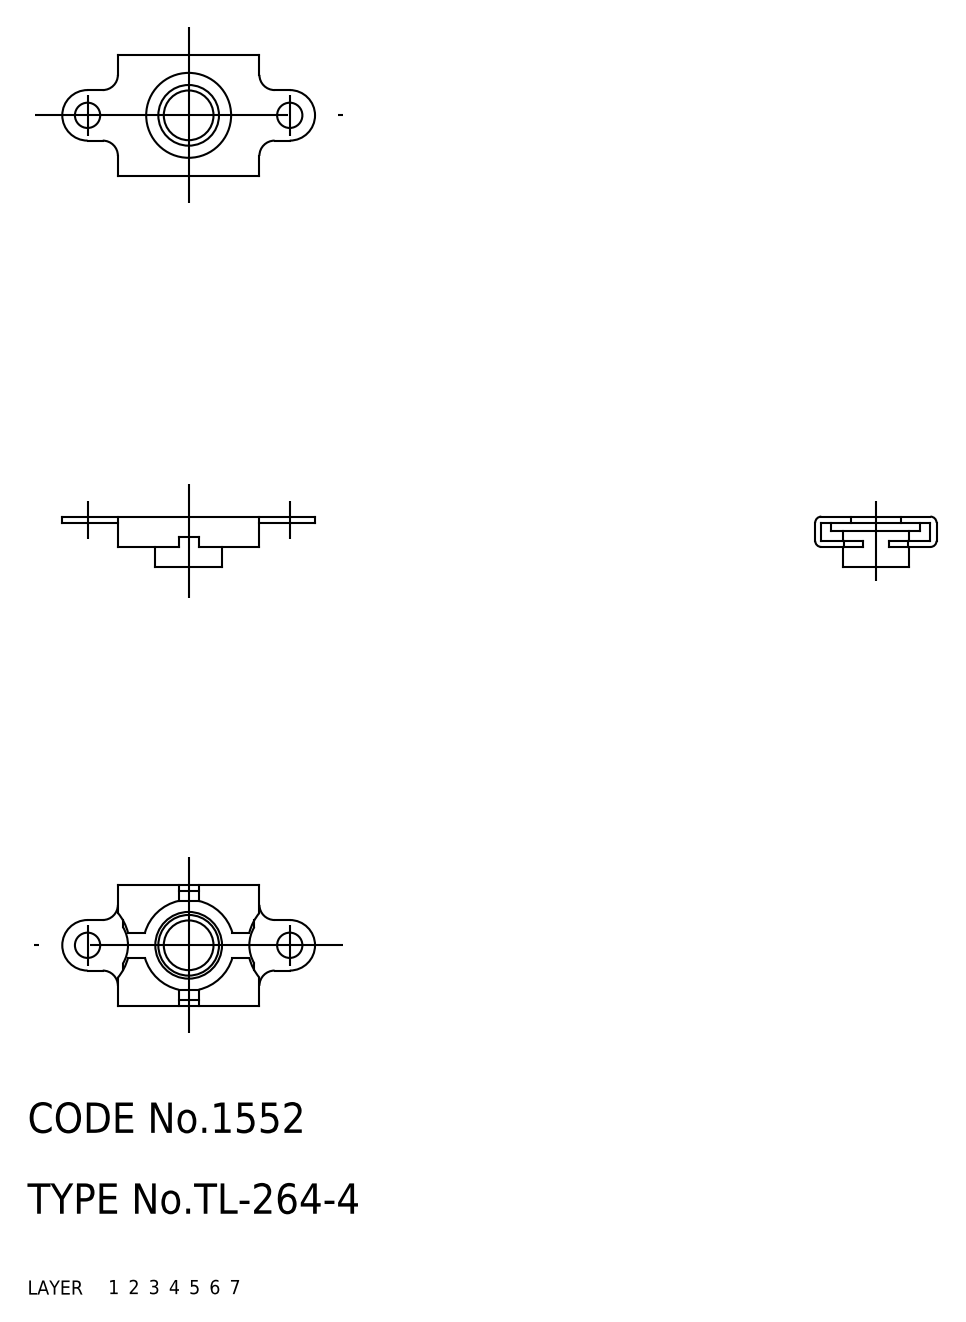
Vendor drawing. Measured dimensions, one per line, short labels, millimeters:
name: nut; housing; TL_264_4_2054_36
written by: CADfix (AUTOMOTIVE_DESIGN)
unit: mm
bodies: 2 solids, 81 faces (0 planar, 0 cylindrical, 81 other)
size: 25 × 12 × 5
volume: 251 mm³; area: 985 mm²
